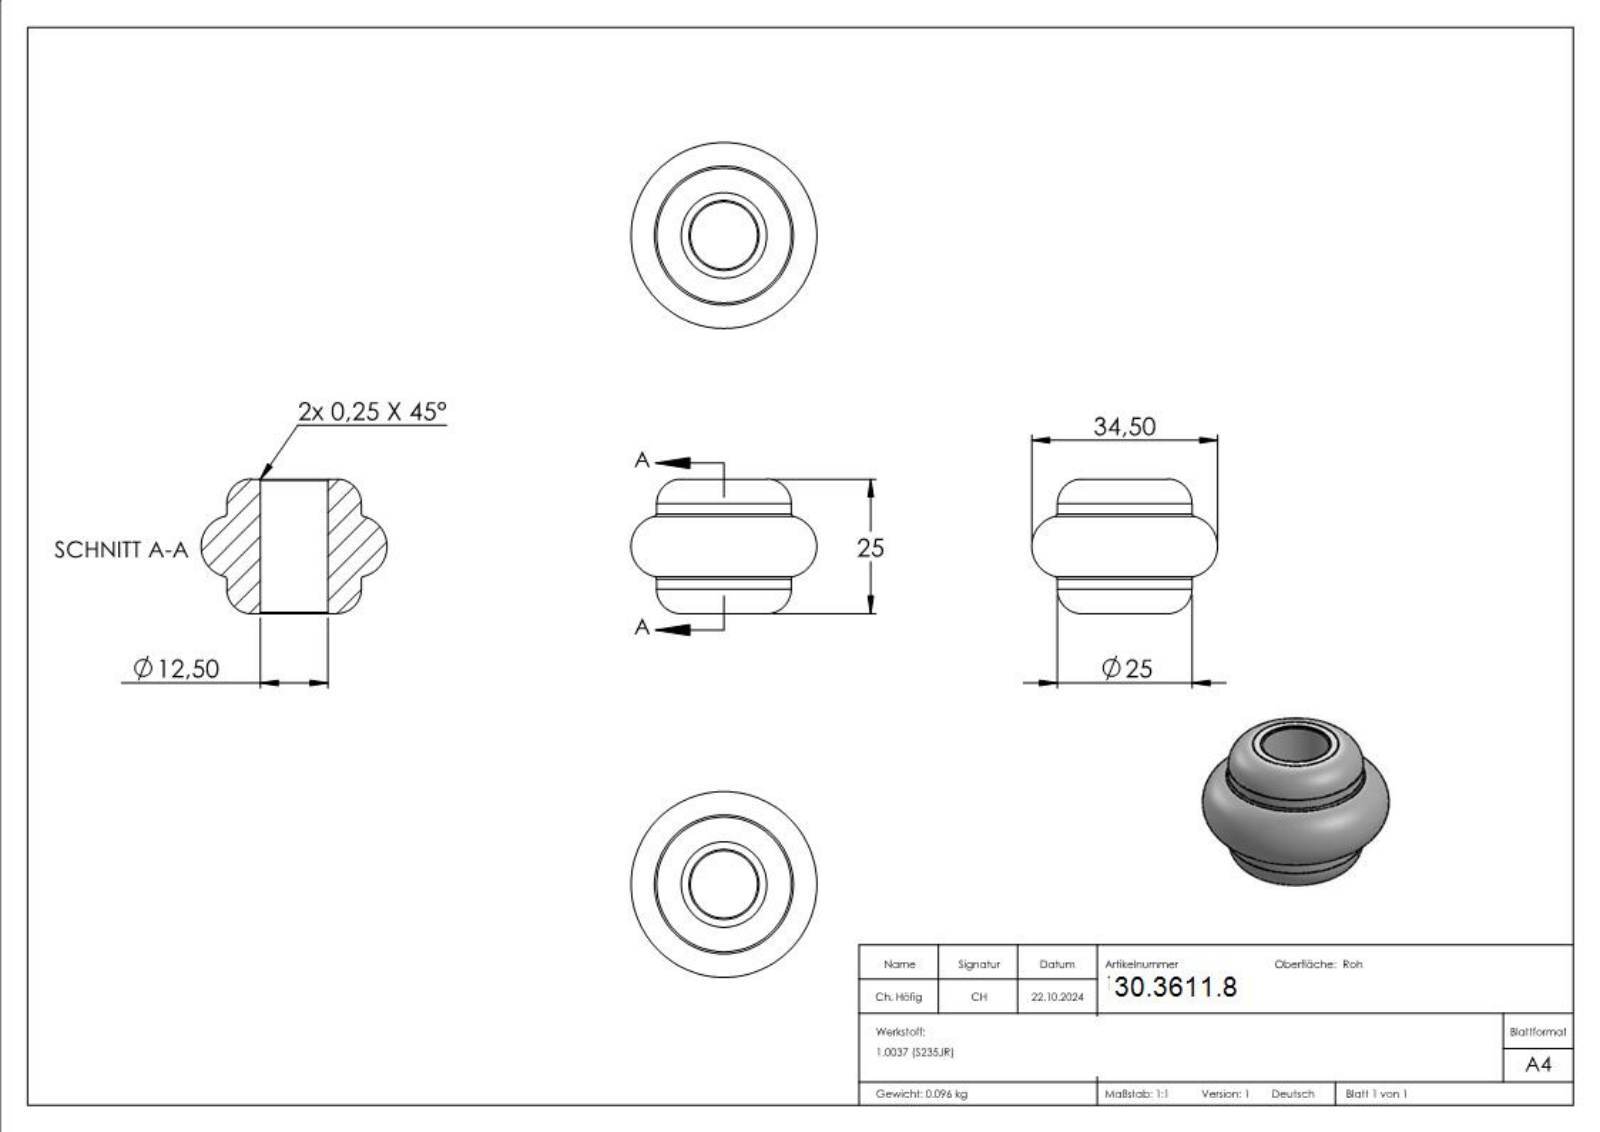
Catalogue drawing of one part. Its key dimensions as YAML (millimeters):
part_name: "1380"
step_written_by: "SolidWorks 2018 (CONFIG_CONTROL_DESIGN)"
units: millimeters
bodies: {solids: 1, faces: 12, planar: 2, cylindrical: 3, other: 7}
overall_size: [34.5, 34.5, 25]
volume: 12248
surface_area: 4004
round_holes:
  - {diameter: 12.5, count: 1}
round_bosses_or_shafts:
  - {diameter: 25, count: 1}
face_to_face_distances: [25]
